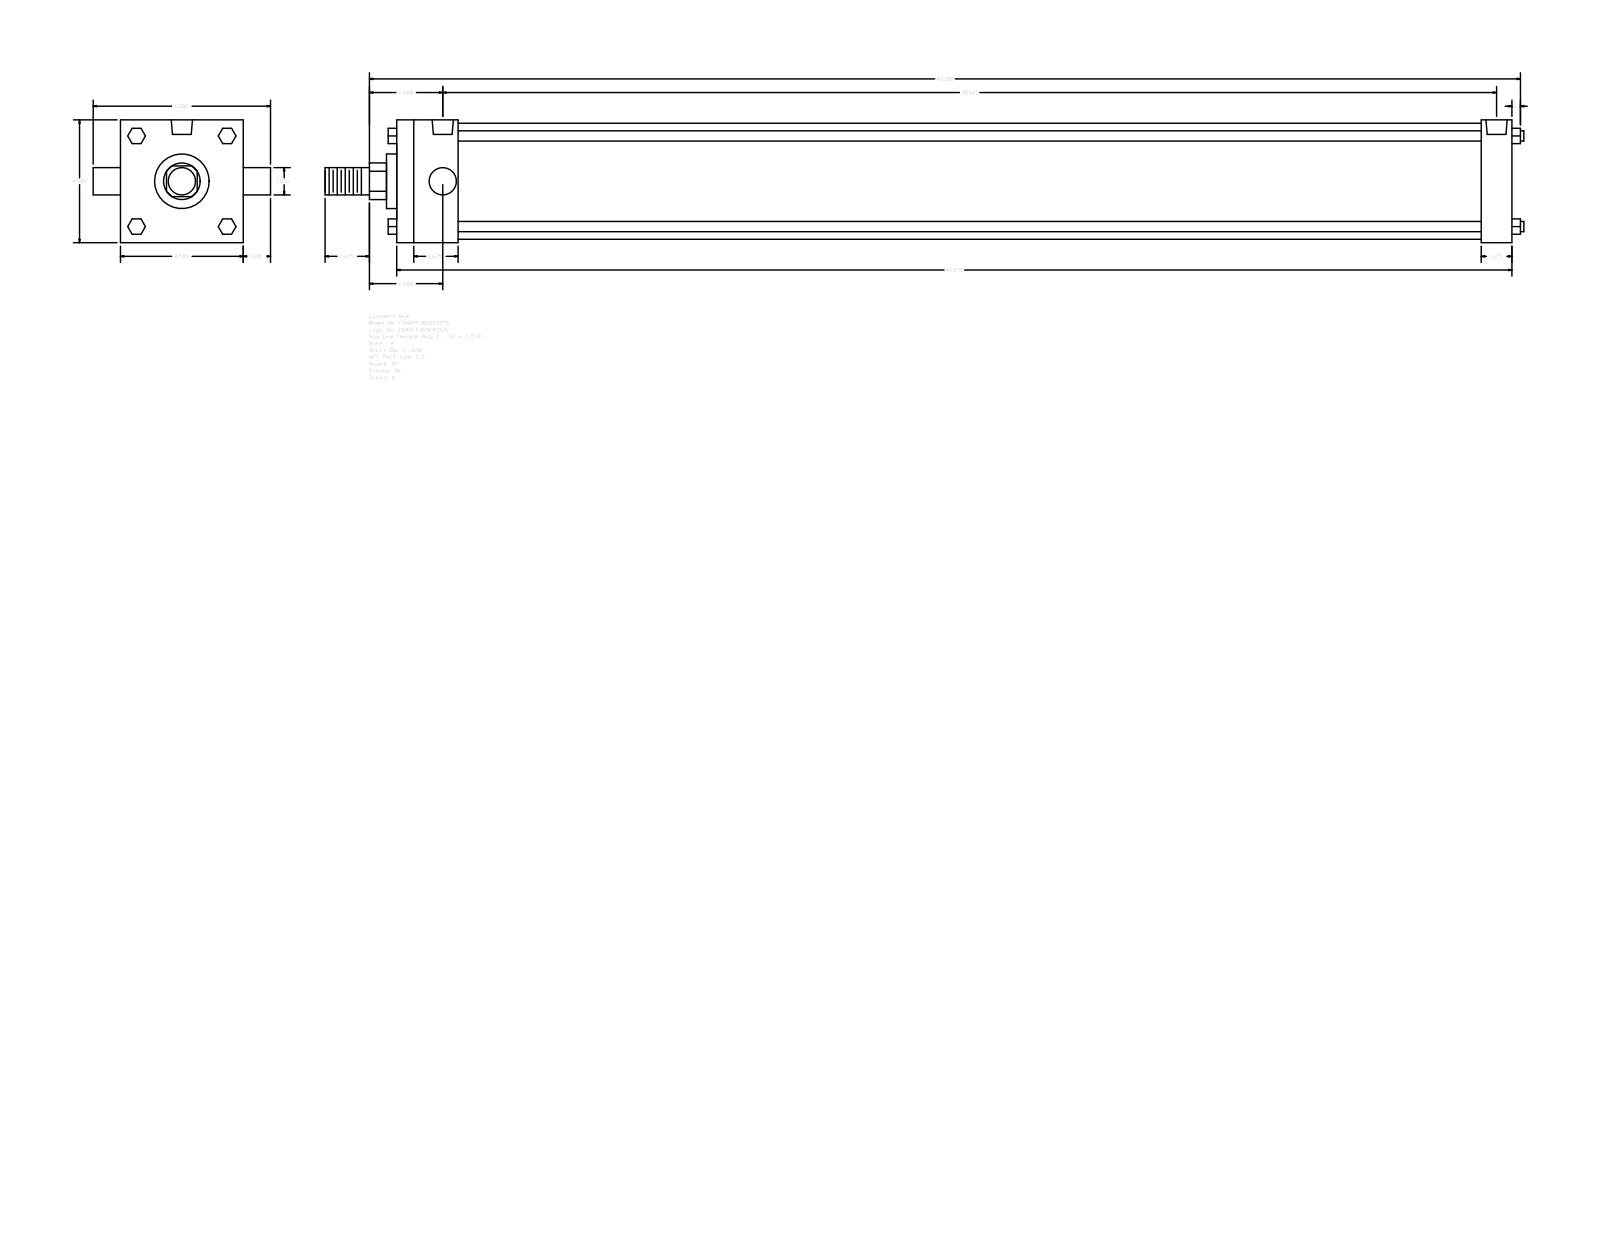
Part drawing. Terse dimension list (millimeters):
name: A_TF__0400_1.375
written by: GSSL Pune (CONFIG_CONTROL_DESIGN)
unit: mm
bodies: 0 solids, 120 faces (92 planar, 28 cylindrical, 0 other)
size: 1116.01 × 165.1 × 114.3
holes: 3× ⌀8.73, 2× ⌀19.77
bosses: 4× ⌀9.53, 2× ⌀25.4, 1× ⌀107.95, 1× ⌀50.8, 1× ⌀34.92
rounds: 1× R17.06
face distances: 114.3, 1038.22, 57.15, 1009.65, 28.57, 952.5, 981.07, 66.67, 14.29, 25.4
hole spacings: 3.18, 977.9, 974.72, 981.08
